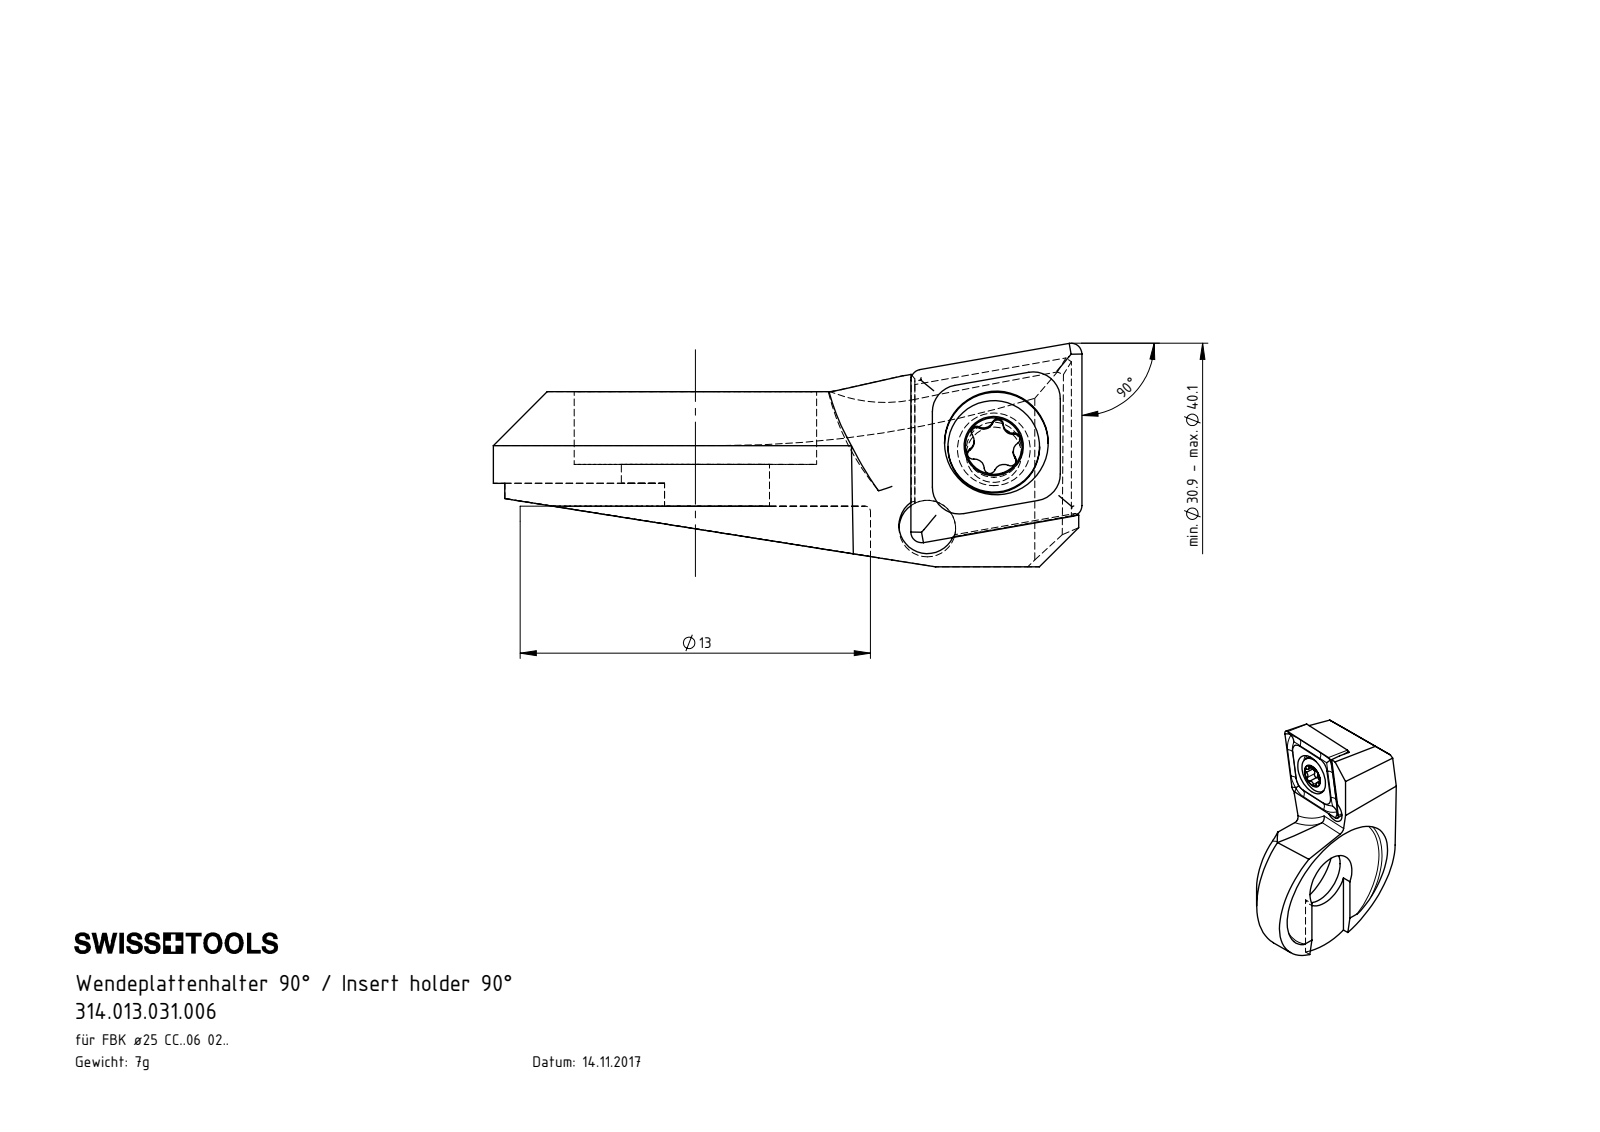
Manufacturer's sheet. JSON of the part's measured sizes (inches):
{"part_name": "F25-WCA.001.006_C_fertigbearbeitet; CCMT060204; WCA-ER2.001.006_A; 314.013.031.006", "step_written_by": "SolidWorks 2017 (CONFIG_CONTROL_DESIGN)", "units": "inches", "bodies": {"solids": 5, "faces": 147, "planar": 48, "cylindrical": 45, "other": 54}, "overall_size": [0.86, 0.591, 0.327], "volume_in3": 0.053, "surface_area_in2": 2.032, "round_holes": [[0.081, 1], [0.083, 1], [0.11, 1], [0.152, 1], [0.217, 1], [0.354, 1]], "round_bosses_or_shafts": [[0.134, 1], [0.098, 1]], "partial_cylinders_radius": [[0.008, 6], [0.014, 5], [0.02, 2], [0.014, 1], [0.041, 1], [0.252, 1], [0.256, 1], [0.295, 1]], "face_to_face_distances": [0.167, 0.163, 0.089, 0.106, 0.102, 0.061, 0.09, 0.134, 0.13, 0.028], "hole_center_spacings": [0.151, 0.157]}
